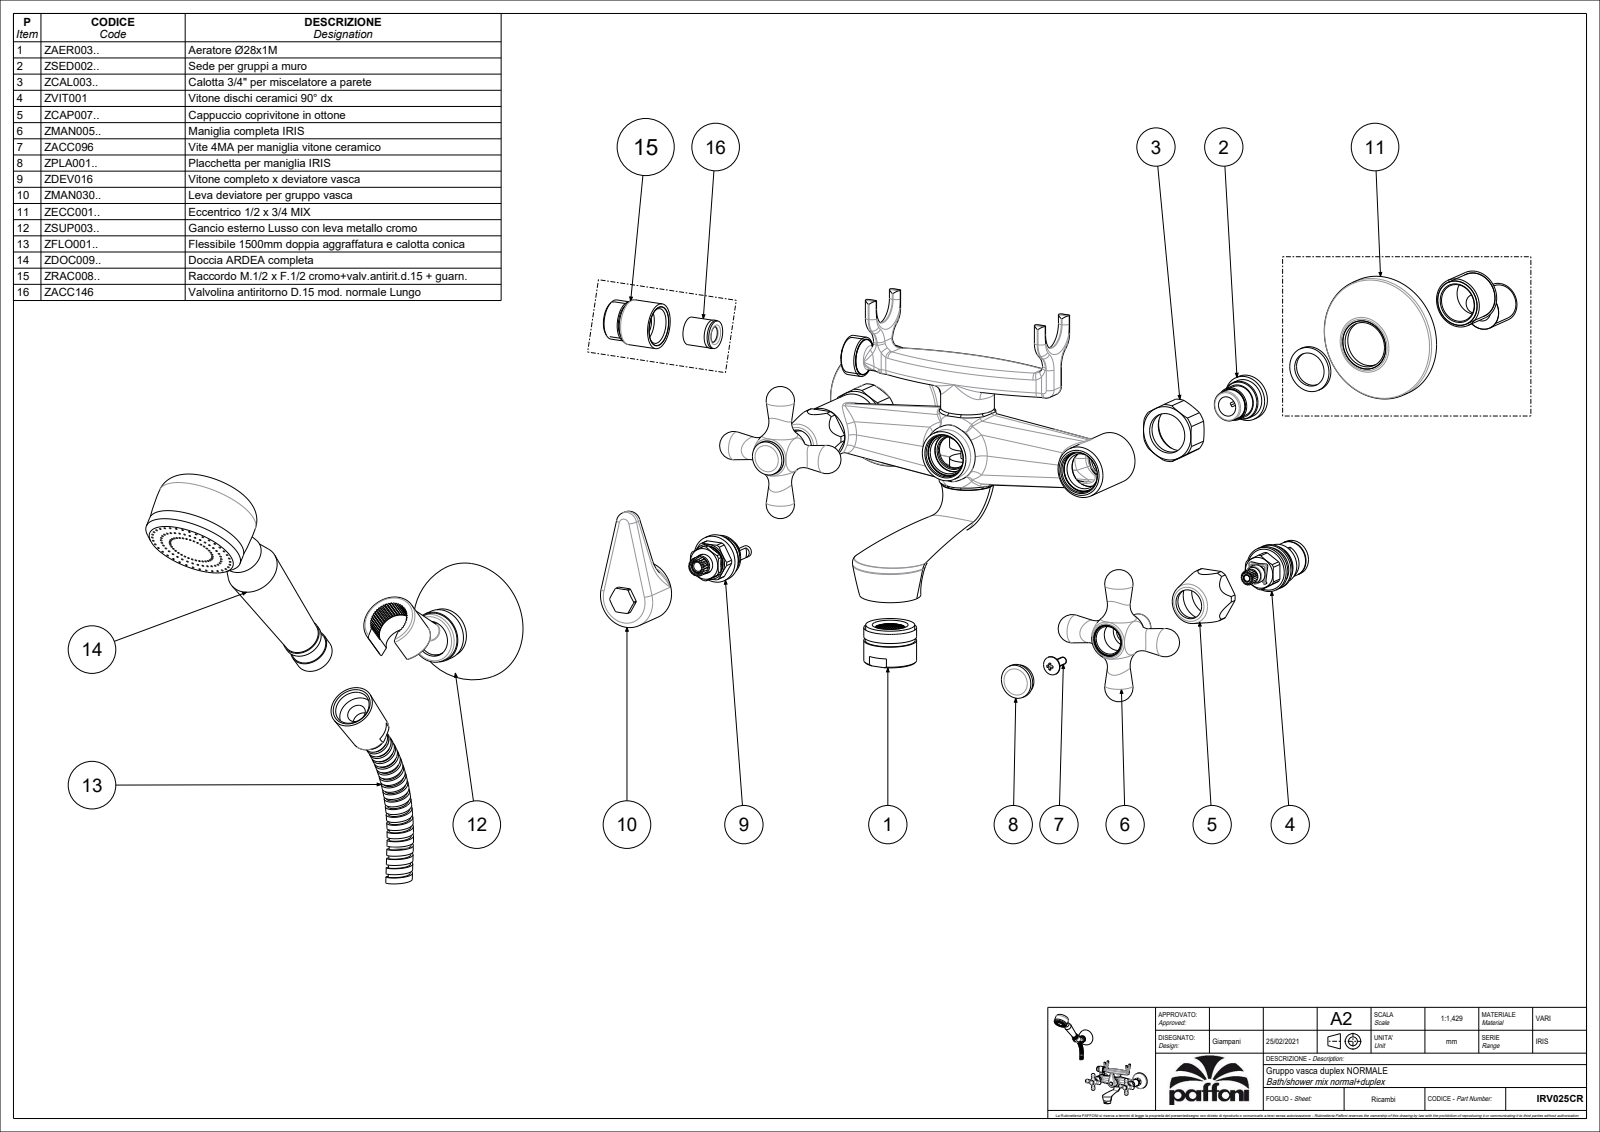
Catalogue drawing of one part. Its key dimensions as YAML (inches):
part_name: "IRV025CR"
step_written_by: "CREO PARAMETRIC BY PTC INC, 2020044 (CONFIG_CONTROL_DESIGN)"
units: inches
bodies: {solids: 5, faces: 1013, planar: 137, cylindrical: 192, other: 684}
overall_size: [14.599, 12.815, 9.186]
volume: 34.94
surface_area: 237
round_holes:
  - {diameter: 0.669, count: 2}
  - {diameter: 0.733, count: 2}
  - {diameter: 0.748, count: 2}
  - {diameter: 0.846, count: 2}
  - {diameter: 0.598, count: 1}
  - {diameter: 0.606, count: 1}
  - {diameter: 0.677, count: 1}
  - {diameter: 0.807, count: 1}
  - {diameter: 0.89, count: 1}
  - {diameter: 0.965, count: 1}
  - {diameter: 1.004, count: 1}
round_bosses_or_shafts:
  - {diameter: 2.579, count: 2}
  - {diameter: 1.083, count: 2}
  - {diameter: 1.063, count: 2}
  - {diameter: 0.709, count: 2}
  - {diameter: 0.531, count: 2}
  - {diameter: 2.106, count: 1}
  - {diameter: 1.24, count: 1}
  - {diameter: 1.142, count: 1}
partial_cylinders:
  - {radius: 0.118, count: 24}
  - {radius: 0.394, count: 9}
  - {radius: 0.059, count: 4}
  - {radius: 0.197, count: 4}
  - {radius: 0.236, count: 3}
  - {radius: 0.404, count: 3}
  - {radius: 0.571, count: 2}
  - {radius: 0.591, count: 2}
face_to_face_distances: [1.516, 1.339, 0.512, 2.854, 1.142, 4.252, 0.906, 3.157, 4.063, 2.724]
hole_center_spacings: [3.11, 3.228, 6.22]
